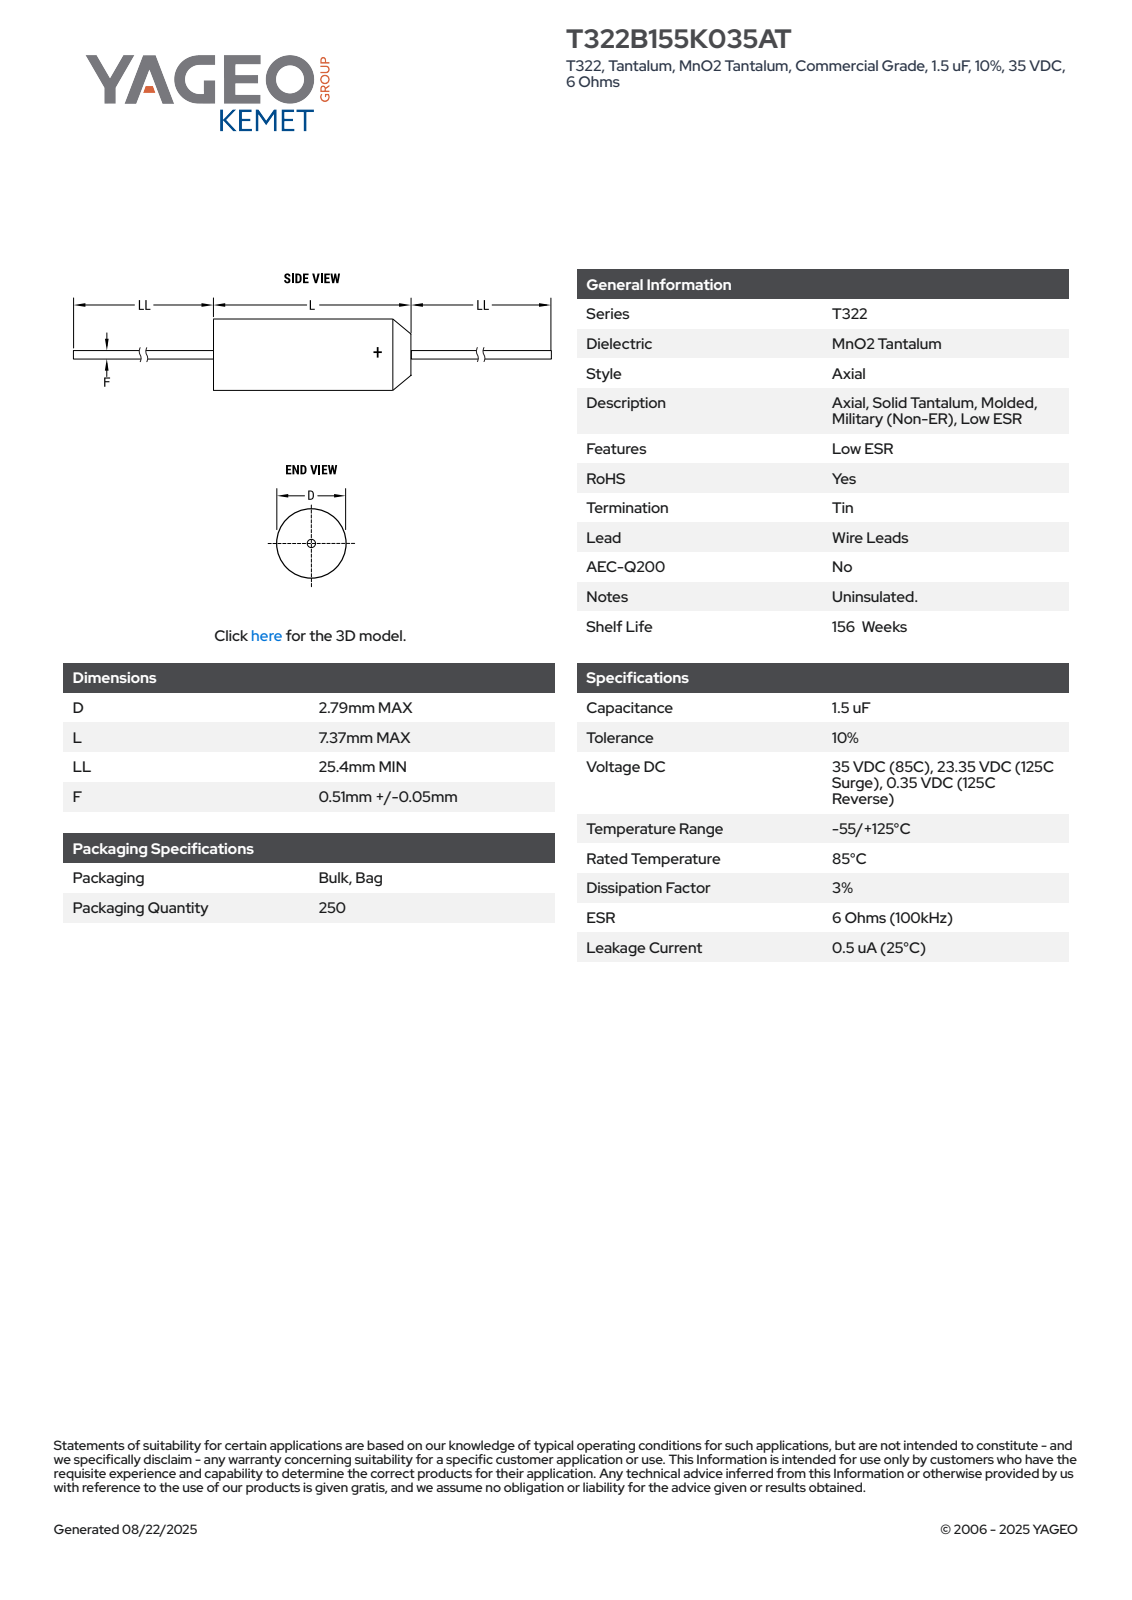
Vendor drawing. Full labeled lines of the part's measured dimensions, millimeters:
Part name (STEP PRODUCT): CTAM_D2.79L7.37LL25.4F0.56
STEP written by: SolidWorks 2020 (AUTOMOTIVE_DESIGN)
Units: millimetres
Bodies: 1 solid, 102 faces (38 planar, 25 cylindrical, 39 other)
Overall size (bounding box): 58.17 × 2.79 × 2.79
Volume: 55 mm³ · Surface area: 162 mm²
Round bosses / shafts (diameter × count): ⌀2.79 ×1, ⌀0.56 ×1
Partial cylindrical surfaces — rounded edges, fillets, slot ends (radius × count): R1.39 ×1
Main face-to-face distances: 7.37, 25.4, 32.77, 58.17, 31.17, 5.77, 1.6, 27, 31.07, 5.67
